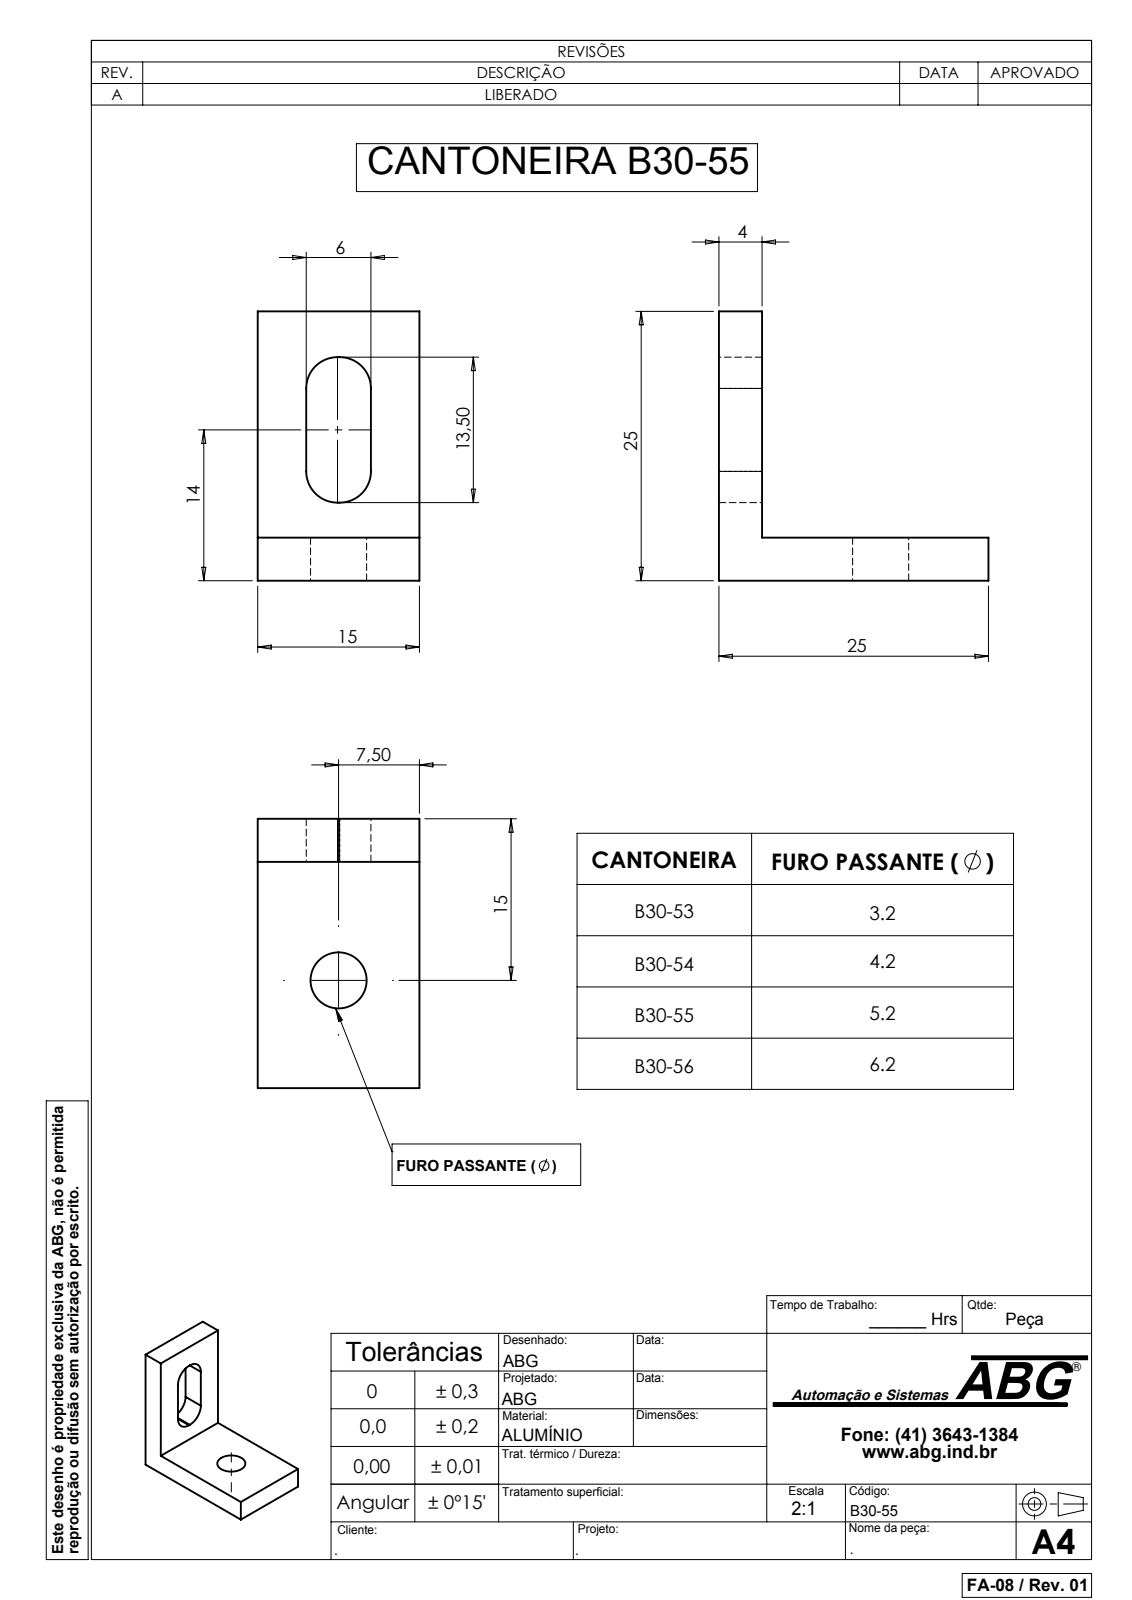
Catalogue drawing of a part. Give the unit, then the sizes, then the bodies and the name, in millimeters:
Units: millimetres
Overall size (bounding box): 25 × 25 × 15
Round holes (diameter × count): ⌀4.2 ×1
Partial cylindrical surfaces — rounded edges, fillets, slot ends (radius × count): R2.9 ×4
Main face-to-face distances: 4, 15, 25, 21, 4.5, 10.5, 6, 7.25, 20.75, 3.25
Volume: 2 409 mm³ · Surface area: 1 882 mm²
Bodies: 1 solid, 18 faces (12 planar, 6 cylindrical, 0 other)
Part name (STEP PRODUCT): B30-54
STEP written by: SolidWorks 2007 (CONFIG_CONTROL_DESIGN)
